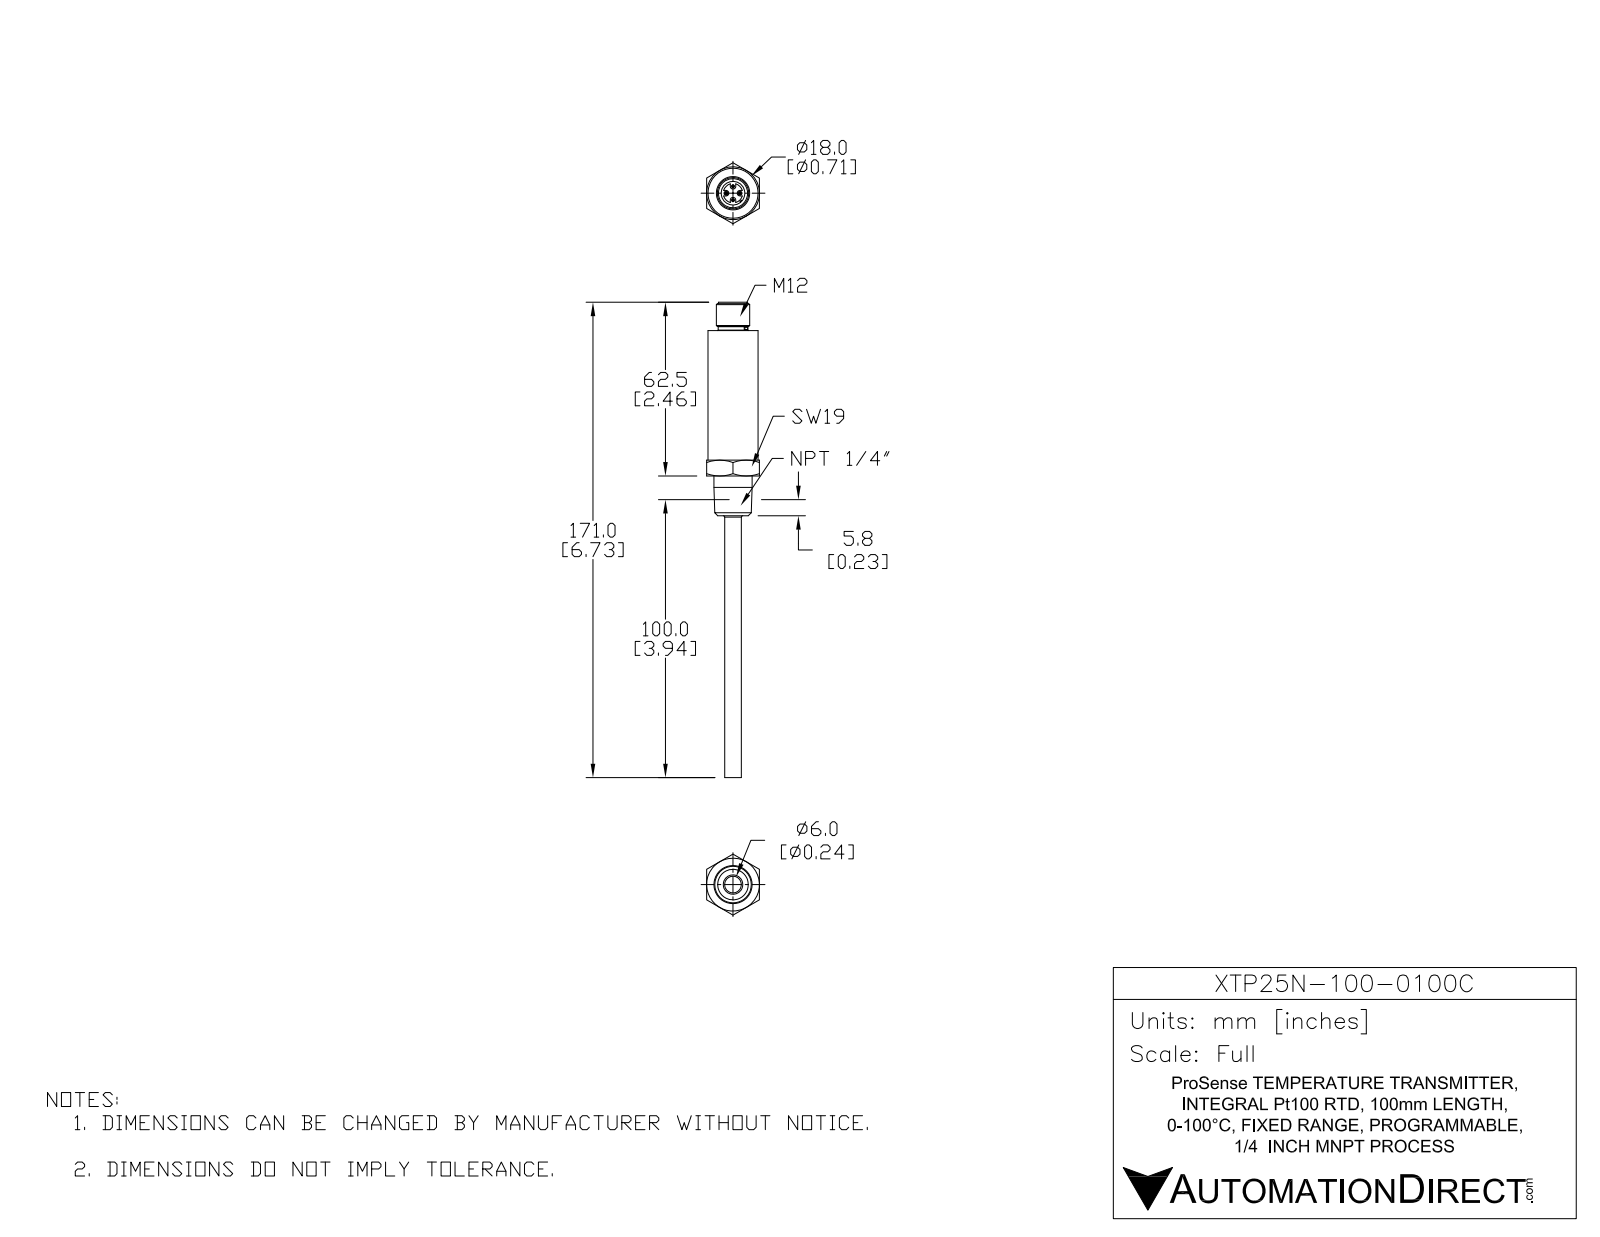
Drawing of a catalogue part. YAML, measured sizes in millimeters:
part_name: "XTP25N-100-0100C"
step_written_by: "SolidWorks 2015 (AUTOMOTIVE_DESIGN)"
units: millimeters
bodies: {solids: 1, faces: 117, planar: 43, cylindrical: 34, other: 40}
overall_size: [171, 21.94, 19]
volume: 18646
surface_area: 6946
round_holes:
  - {diameter: 4, count: 1}
  - {diameter: 8.5, count: 1}
round_bosses_or_shafts:
  - {diameter: 1.02, count: 4}
  - {diameter: 18, count: 1}
  - {diameter: 13.72, count: 1}
  - {diameter: 12, count: 1}
  - {diameter: 10.7, count: 1}
  - {diameter: 10.5, count: 1}
  - {diameter: 6, count: 1}
partial_cylinders:
  - {radius: 1, count: 4}
  - {radius: 3.5, count: 1}
  - {radius: 4.25, count: 1}
face_to_face_distances: [19, 52.3, 14.3, 66.6, 20, 5.7, 46.6, 76.8, 62.5, 56.8]
